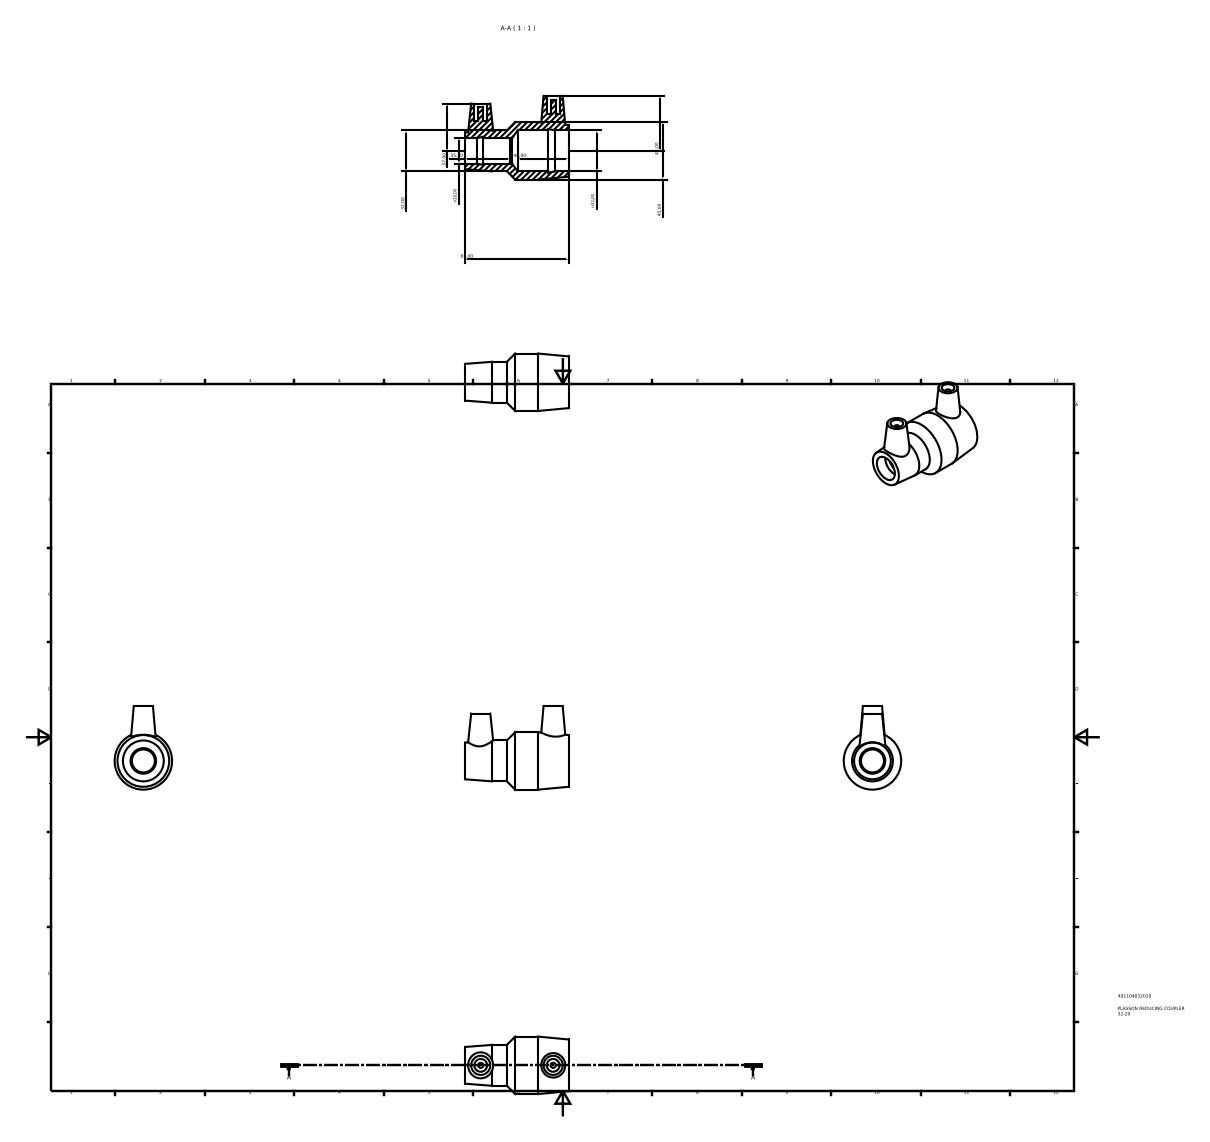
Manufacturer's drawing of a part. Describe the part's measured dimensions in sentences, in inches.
The part is named "491104032020". Its 3-D file was written by "Autodesk Inventor 2015 (AUTOMOTIVE_DESIGN)". It is 1 solid with 32 faces: 12 planar, 11 cylindrical and 9 other. Overall it measures 3.189 by 2.579 by 1.772 inches. Its volume is 3.494 cubic inches and its surface area 33.42 square inches. Round holes: 2 of diameter 0.394, 1 of diameter 0.709, 1 of diameter 0.787, 1 of diameter 1.26. Round bosses or shafts: 2 of diameter 0.157, 1 of diameter 1.772. The main face-to-face distances are 3.189, 0.551, 0.236, 2.559, 0.63, 0.787, 0.315, 2.008, 2.638, 1.447. The hole center spacings are 2.232.
